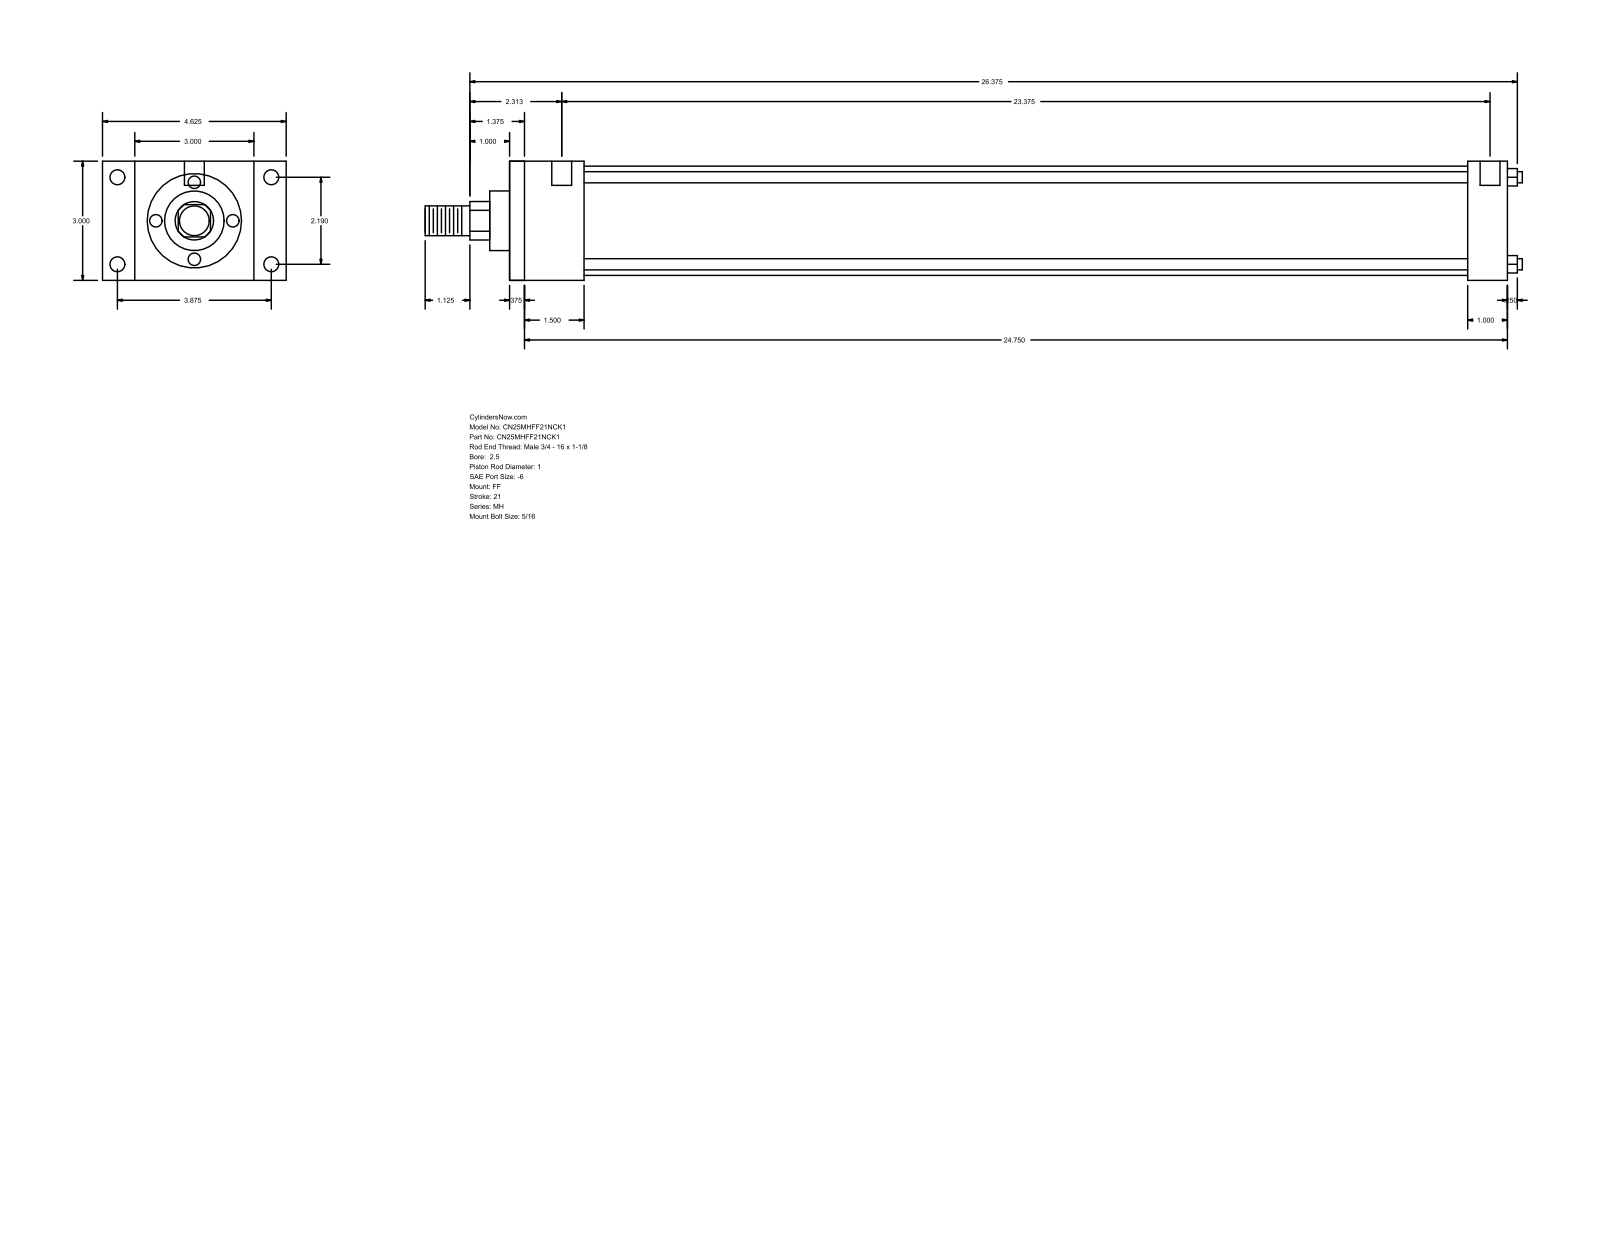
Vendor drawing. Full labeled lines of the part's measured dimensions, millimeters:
Part name (STEP PRODUCT): MH_FF__0250_1
STEP written by: GSSL Pune (CONFIG_CONTROL_DESIGN)
Units: millimetres
Bodies: 0 solids, 92 faces (64 planar, 28 cylindrical, 0 other)
Overall size (bounding box): 701.67 × 117.47 × 76.2
Round holes (diameter × count): ⌀5.56 ×4, ⌀9.53 ×4, ⌀12.7 ×2
Round bosses / shafts (diameter × count): ⌀7.14 ×4, ⌀69.85 ×1, ⌀38.1 ×1, ⌀25.4 ×1, ⌀19.05 ×1
Partial cylindrical surfaces — rounded edges, fillets, slot ends (radius × count): R12.29 ×1
Main face-to-face distances: 76.2, 638.18, 9.52, 628.66, 47.63, 612.77, 38.11, 603.25, 565.14, 590.55
Hole centre spacings: 55.62, 98.42, 113.05, 601.66, 3.18, 4.76, 593.72, 596.9
